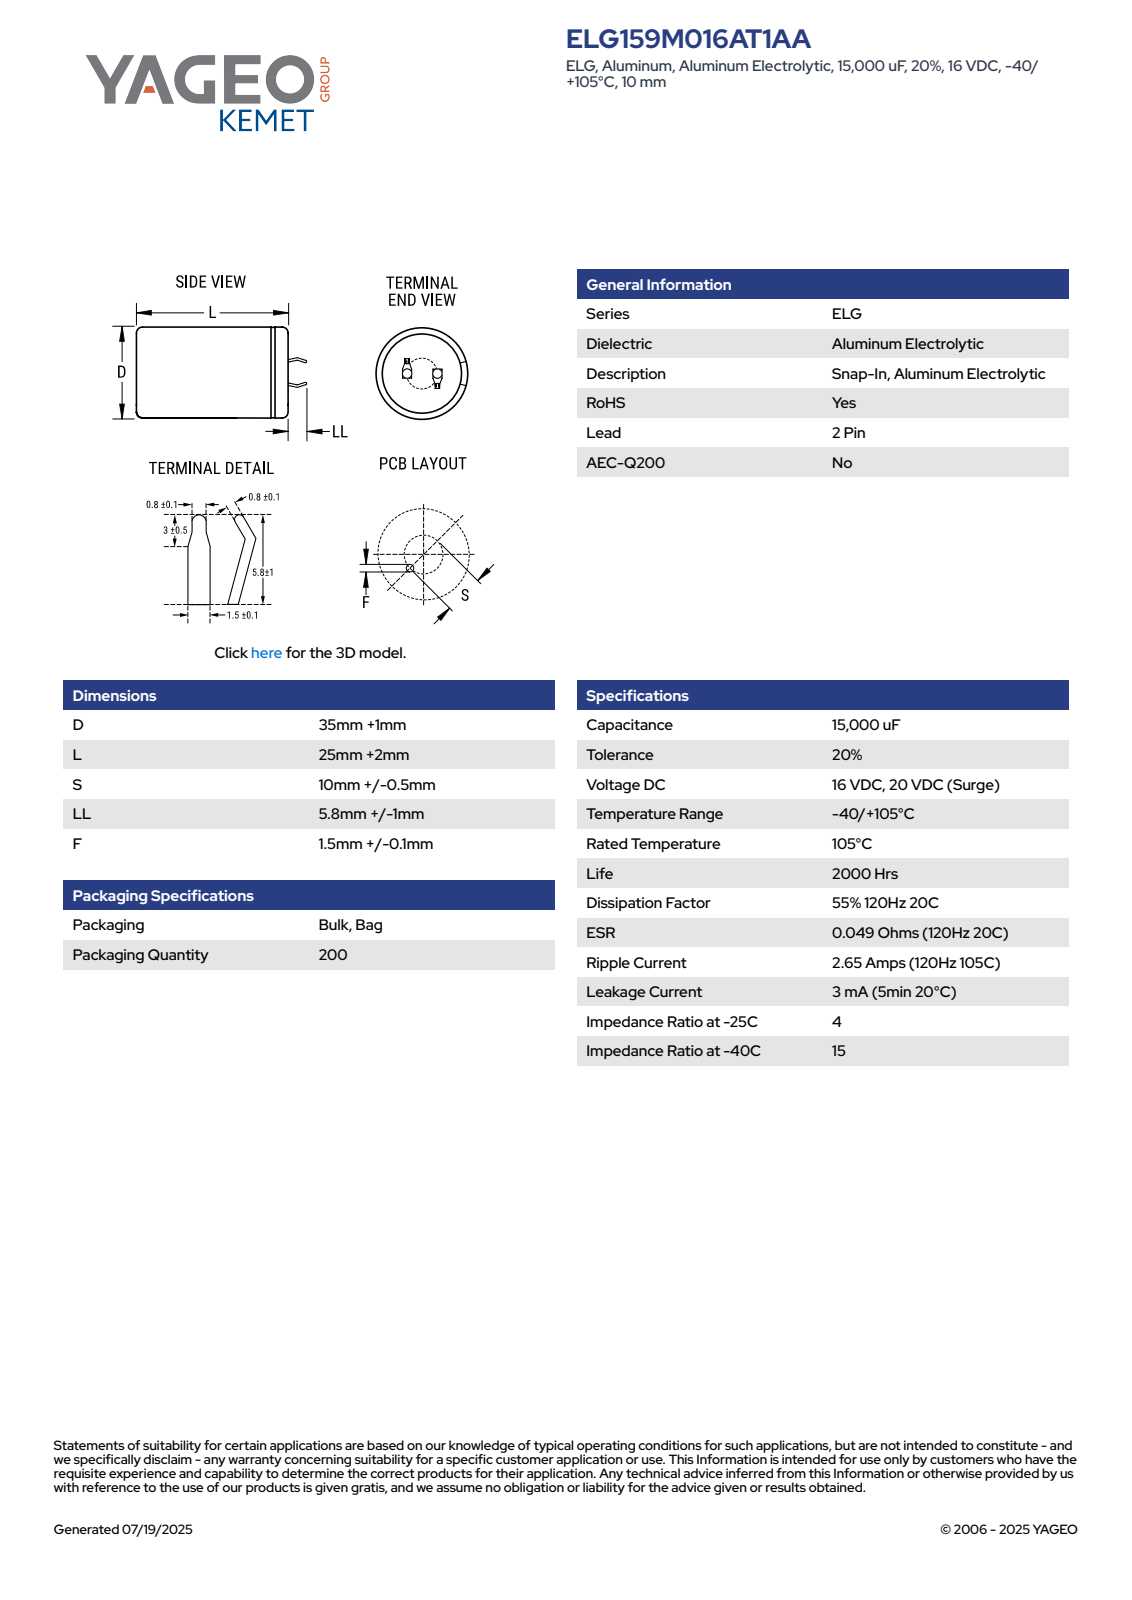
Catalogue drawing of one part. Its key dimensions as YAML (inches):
part_name: "CARS_K2P_35X25_D36L27S10LL6.8F1.6"
step_written_by: "SolidWorks 2014 (AUTOMOTIVE_DESIGN)"
units: inches
bodies: {solids: 1, faces: 100, planar: 52, cylindrical: 9, other: 39}
overall_size: [1.417, 1.417, 1.33]
volume: 1.645
surface_area: 7.88
round_holes:
  - {diameter: 1.254, count: 1}
round_bosses_or_shafts:
  - {diameter: 1.417, count: 1}
partial_cylinders:
  - {radius: 0.708, count: 1}
face_to_face_distances: [1.063, 1.082, 0.02, 0.024, 0.279, 0.03, 0.053, 0.302, 0.255, 0.023]
